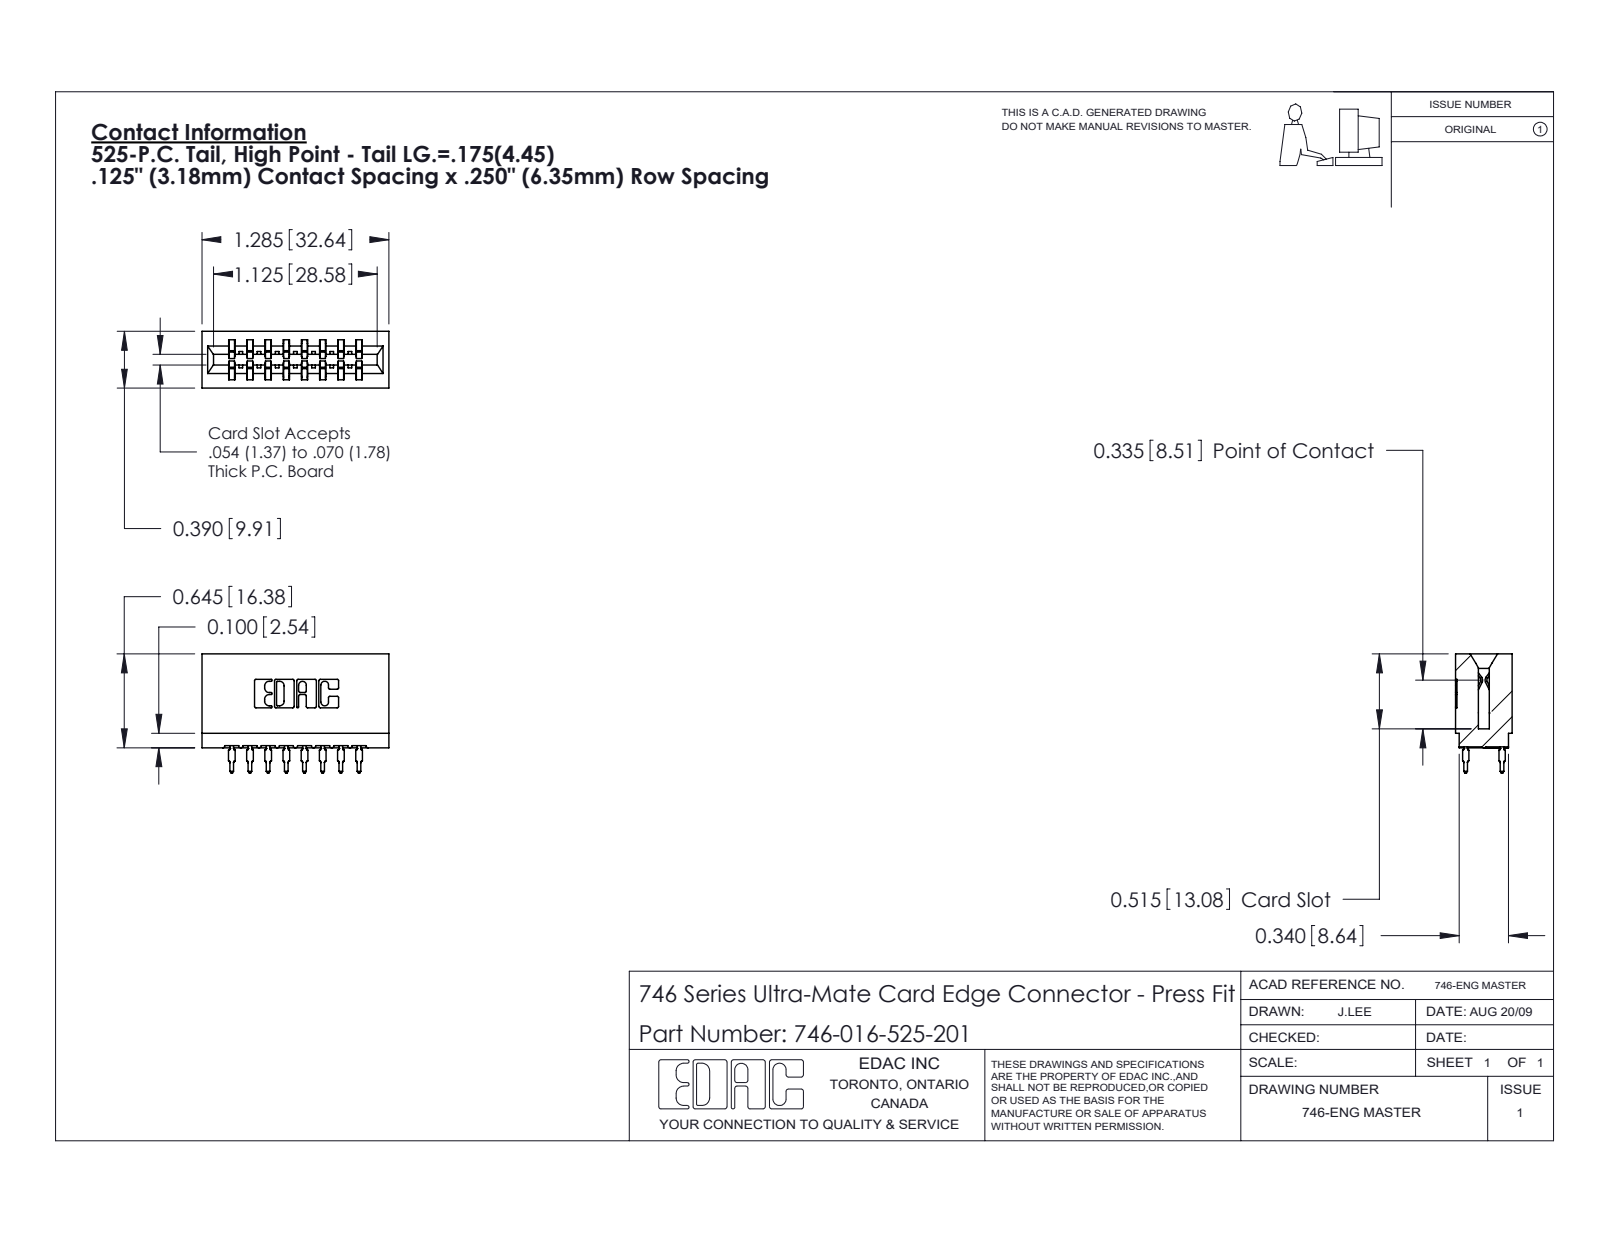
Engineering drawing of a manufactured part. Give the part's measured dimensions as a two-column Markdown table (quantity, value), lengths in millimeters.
| quantity | value |
| --- | --- |
| part name | 746-016-525-201; 746-292-001_525; 746 Part_.515 Slot Depth - 01 |
| STEP written by | SolidWorks 2020 (CONFIG_CONTROL_DESIGN) |
| units | millimeters |
| bodies | 17 solids, 1529 faces (791 planar, 322 cylindrical, 416 other) |
| overall size | 32.6 × 20.8 × 9.9 |
| volume | 3 700 mm³ |
| surface area | 5 234 mm² |
| partial cylindrical surfaces (radius × count) | 0.5 × 32, 0.3 × 22, 0.4 × 9, 0.1 × 8, 0.3 × 8, 0.2 × 6, 0.8 × 6, 0.7 × 3 |
| main face-to-face distances | 6.4, 1.1, 3.2, 12.7, 8.5, 1.4, 7.4, 5.3, 9.5, 3.2 |
